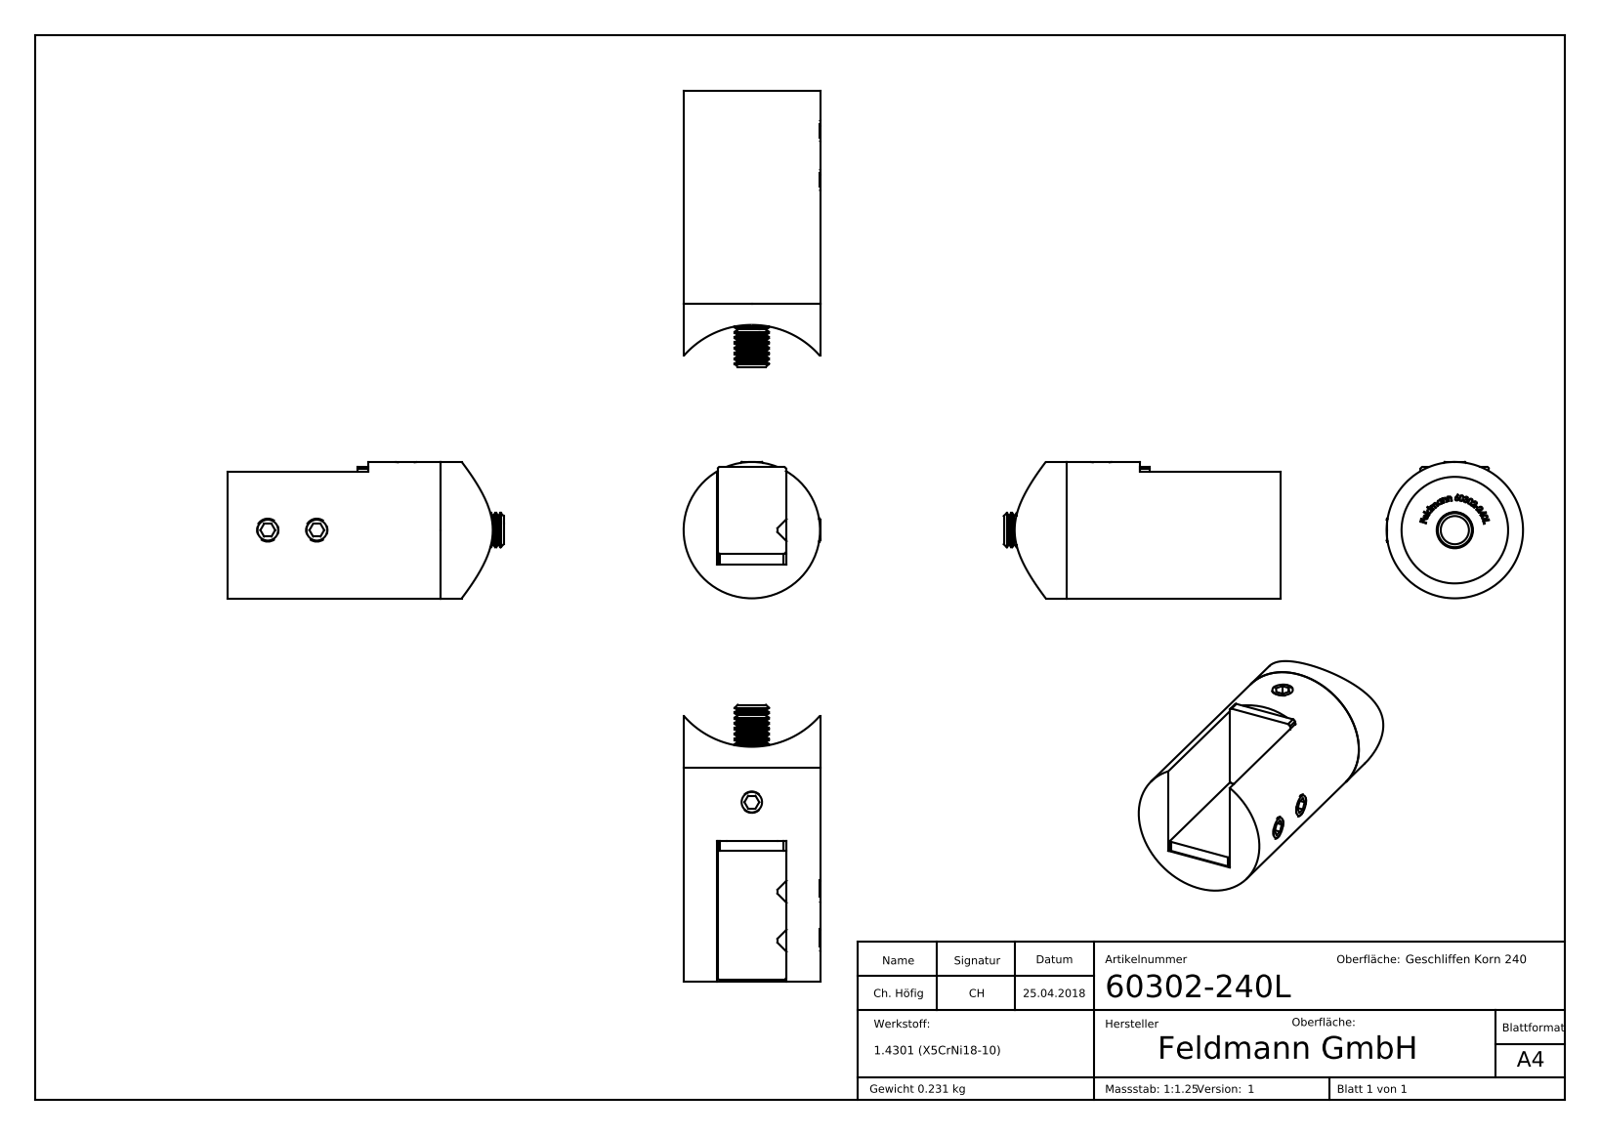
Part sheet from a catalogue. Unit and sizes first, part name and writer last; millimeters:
Units: millimetres
Overall size (bounding box): 70 × 64.85 × 32
Round holes (diameter × count): ⌀5 ×3, ⌀8.5 ×1, ⌀25 ×1
Round bosses / shafts (diameter × count): ⌀6 ×3, ⌀32 ×1, ⌀20 ×1, ⌀15.57 ×1, ⌀8 ×1
Partial cylindrical surfaces — rounded edges, fillets, slot ends (radius × count): R0.5 ×8, R24.15 ×1
Main face-to-face distances: 2.45, 16.3, 17, 3.3, 20.3, 53.3, 50, 33, 22.75, 19.45
Hole centre spacings: 11.5
Volume: 32 394 mm³ · Surface area: 16 864 mm²
Bodies: 8 solids, 429 faces (184 planar, 53 cylindrical, 192 other)
Part name (STEP PRODUCT): 6030X-240X Teil3_6030X-240X Teil3; socket set screw cone point_din_DIN 914 - M6 x 10-S; 6030X-240X Teil1_6030X-240L Teil1; socket countersunk head screw_din (+8 more)
STEP written by: SolidWorks 2018 (CONFIG_CONTROL_DESIGN)
